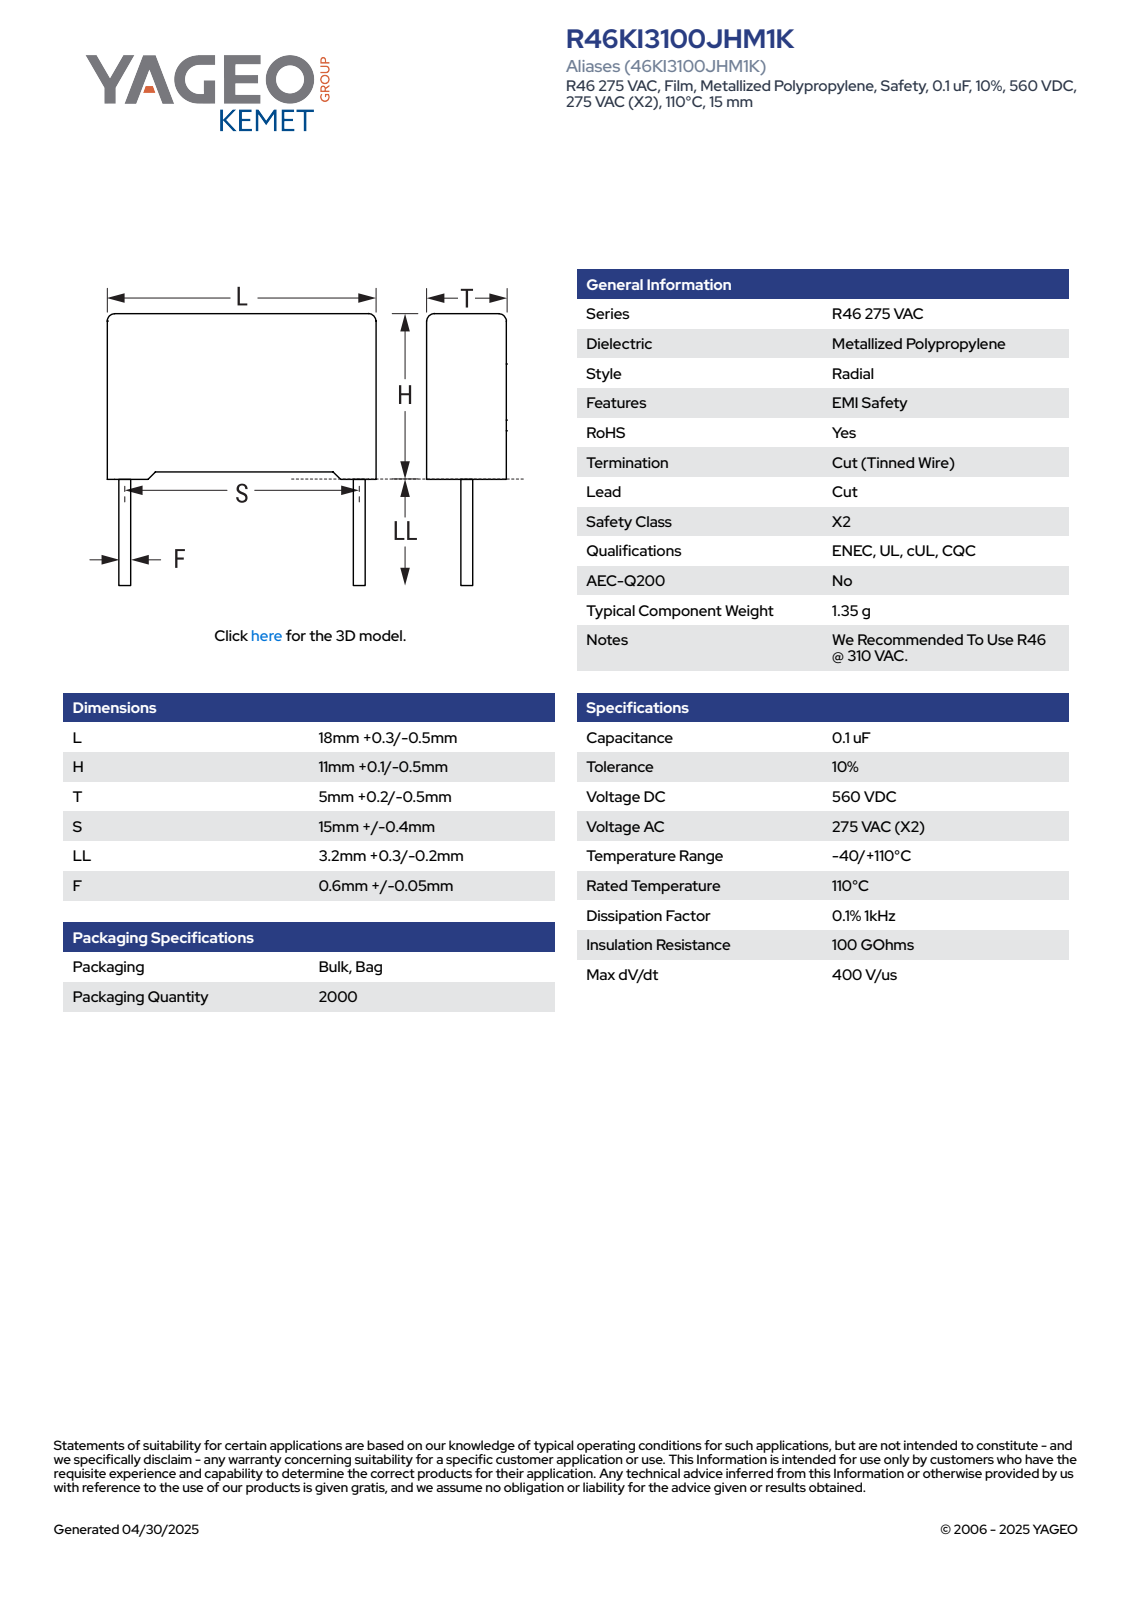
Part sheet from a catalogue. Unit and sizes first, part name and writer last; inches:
Units: inches
Overall size (bounding box): 0.72 × 0.575 × 0.205
Round bosses / shafts (diameter × count): ⌀0.026 ×2
Partial cylindrical surfaces — rounded edges, fillets, slot ends (radius × count): R0.02 ×4
Main face-to-face distances: 0.205, 0.407, 0.72, 0.024, 0.181, 0.015, 0.422, 0.015, 0.03, 0.437
Volume: 0.061 in³ · Surface area: 1.18 in²
Bodies: 4 solids, 85 faces (77 planar, 8 cylindrical, 0 other)
Part name (STEP PRODUCT): CFR_RB2_18X11X5_L18.3H11.1T5.2S15LL3.5F0.65
STEP written by: SolidWorks 2021 (AUTOMOTIVE_DESIGN)
